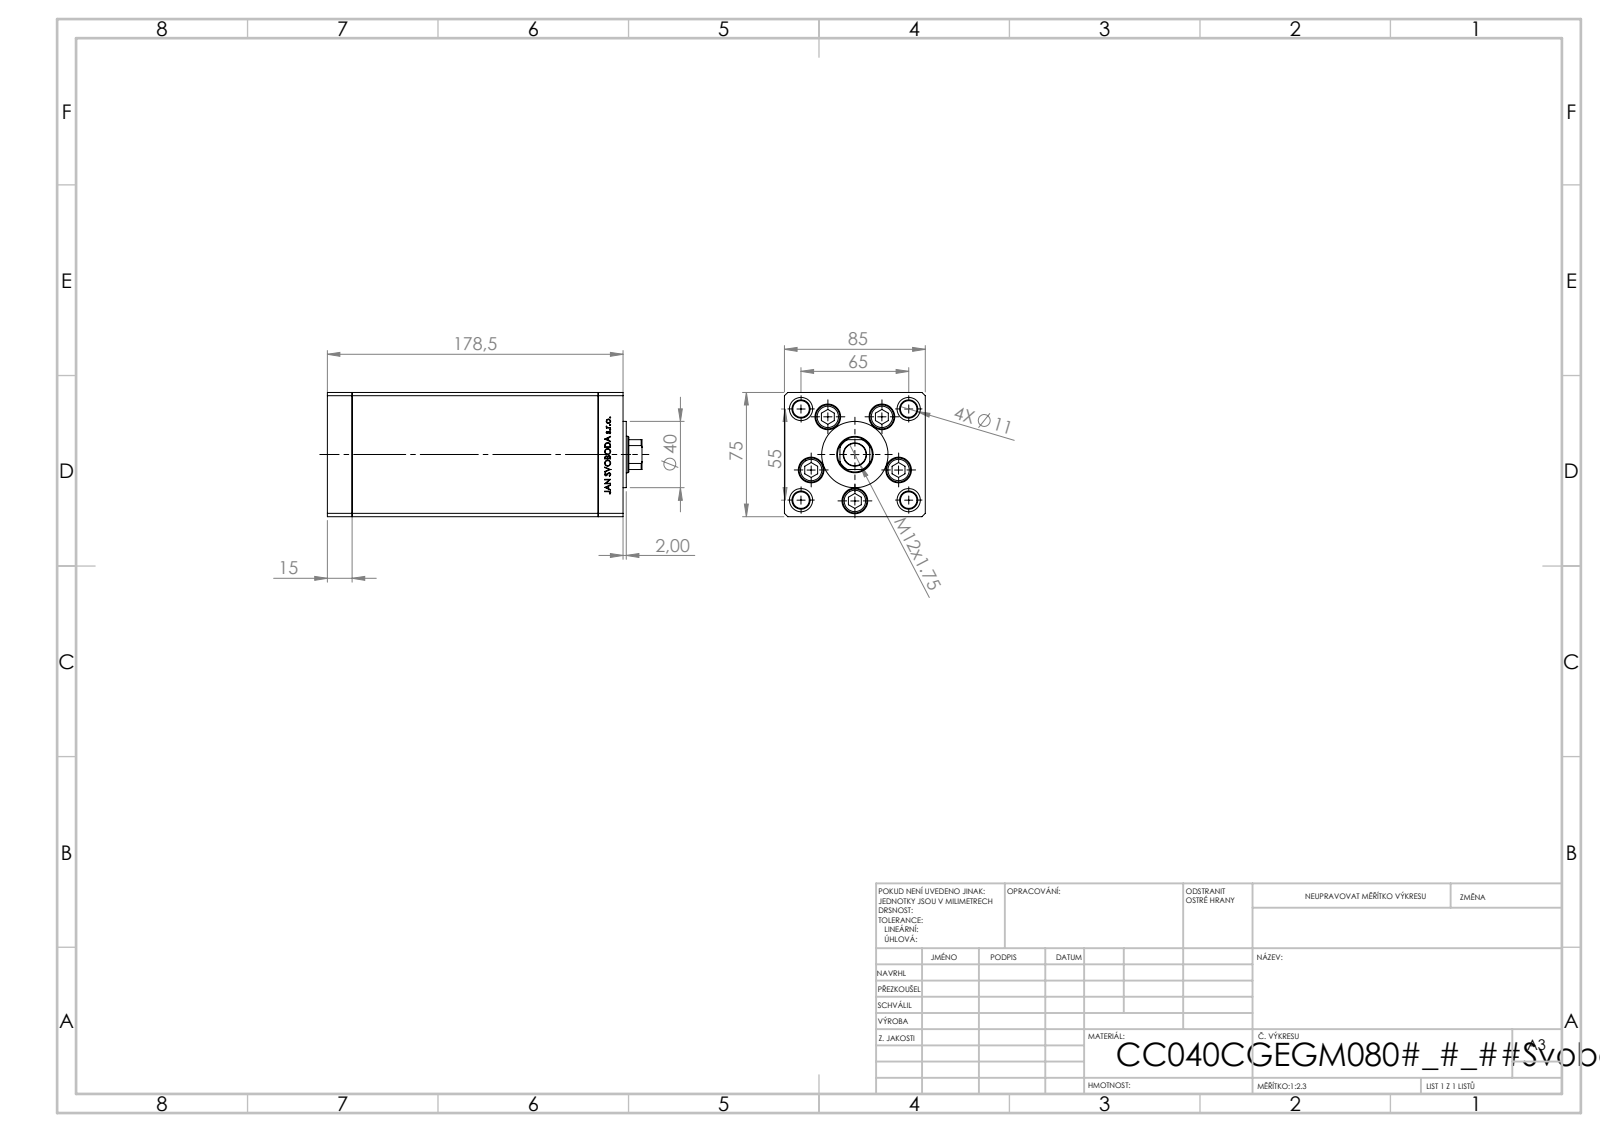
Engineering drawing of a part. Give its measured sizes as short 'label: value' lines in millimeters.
name: V220C_C MIDDLE; V220C FRONT; V220C BACK_C; V220C_VC_C (+1 more)
written by: SolidWorks 2019 (CONFIG_CONTROL_DESIGN)
unit: mm
bodies: 13 solids, 1159 faces (538 planar, 159 cylindrical, 462 other)
size: 190 × 85 × 75
volume: 949 001 mm³; area: 179 253 mm²
holes: 9× ⌀11, 5× ⌀15.5, 4× ⌀10, 4× ⌀14, 1× ⌀13.5, 1× ⌀14.5, 1× ⌀22
bosses: 5× ⌀8, 4× ⌀14.5, 1× ⌀40
rounds: 2× R0.93, 1× R10.5
face distances: 85, 75, 15, 148.5, 163.5, 10.5, 178.5, 34.25, 144.25, 129.25
hole spacings: 28, 42.57, 16.86, 19.17, 32.33, 32.5, 33.63, 37.33
